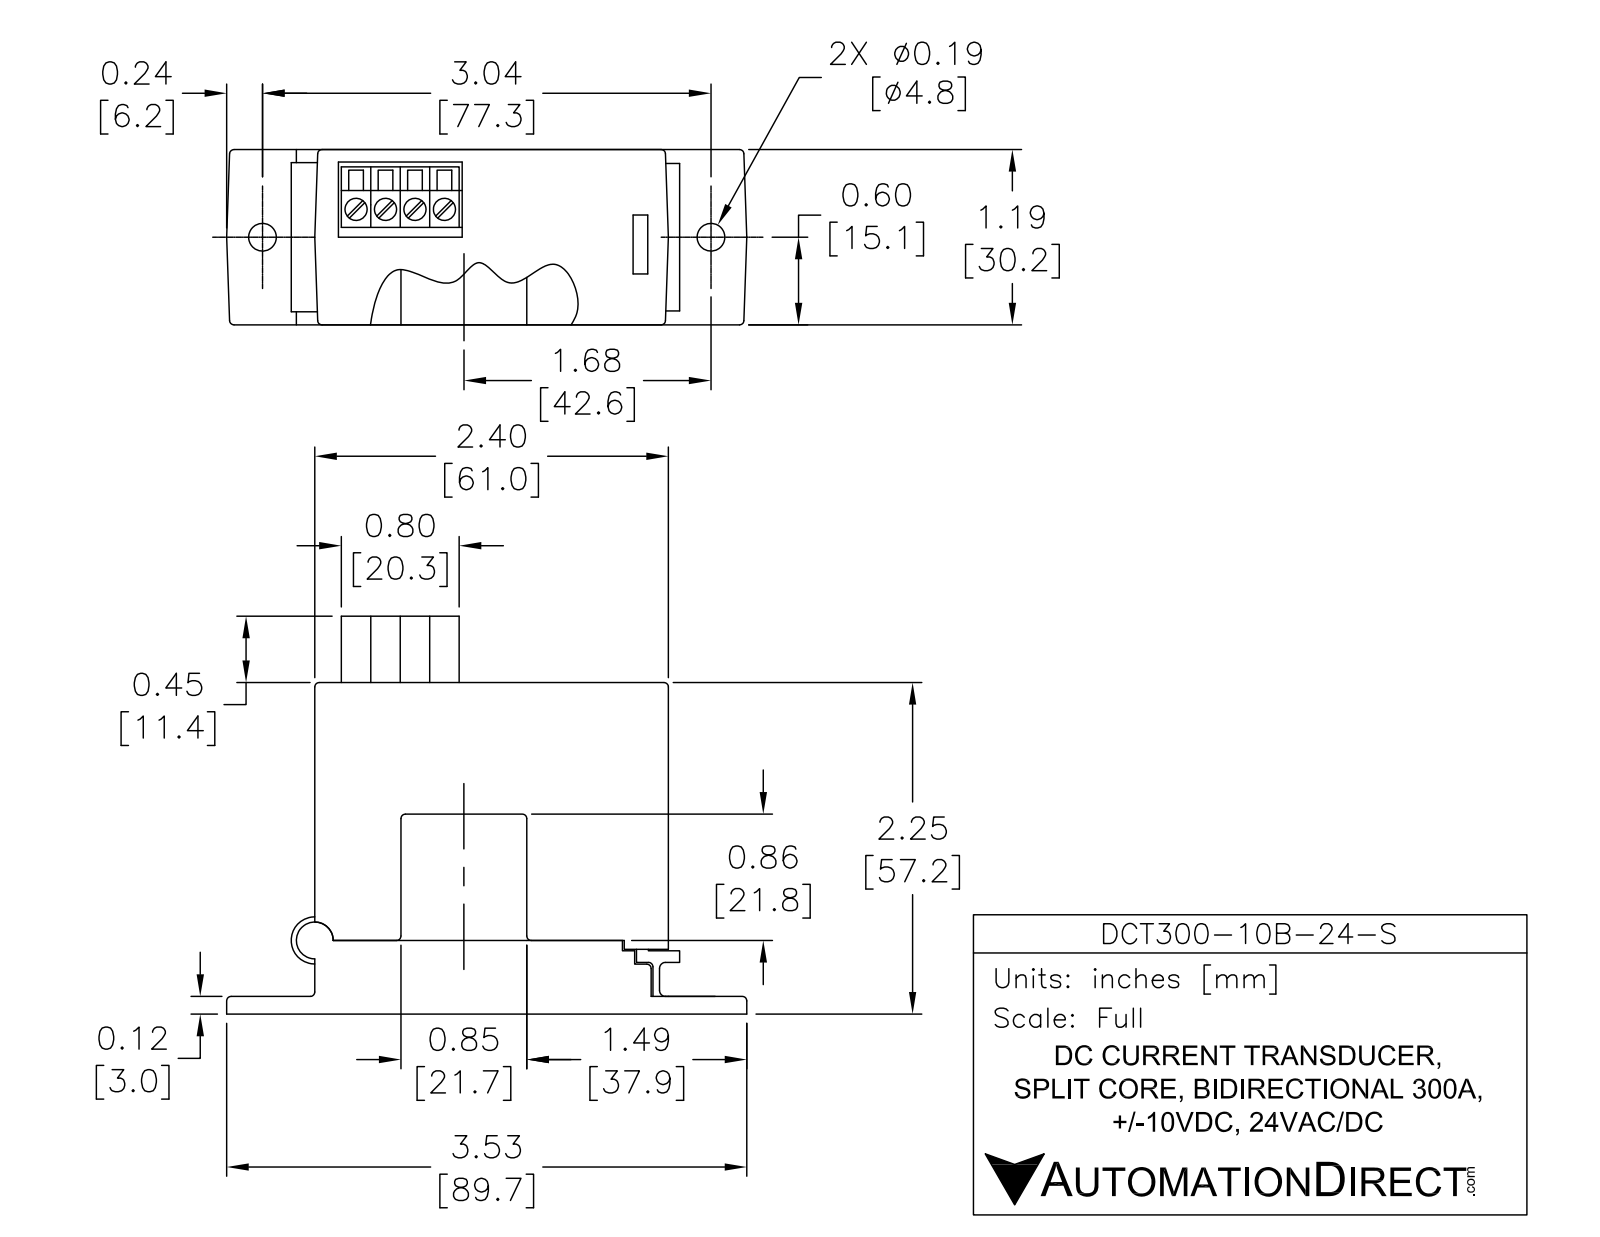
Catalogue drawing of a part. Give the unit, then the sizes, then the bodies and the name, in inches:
Units: inches
Overall size (bounding box): 3.531 × 2.7 × 1.189
Round holes (diameter × count): ⌀0.157 ×4, ⌀0.188 ×2, ⌀0.26 ×1
Round bosses / shafts (diameter × count): ⌀0.25 ×1
Partial cylindrical surfaces — rounded edges, fillets, slot ends (radius × count): R0.03 ×22, R0.16 ×1, R0.17 ×1
Main face-to-face distances: 1.189, 2.252, 0.5, 1.752, 2.399, 0.505, 1.747, 0.118, 0.382, 0.387
Hole centre spacings: 0.197, 0.398, 0.201, 0.596, 0.632, 0.822, 1.019, 1.213
Volume: 5.725 in³ · Surface area: 35.03 in²
Bodies: 4 solids, 158 faces (100 planar, 50 cylindrical, 8 other)
Part name (STEP PRODUCT): DCT300-10B-24-S
STEP written by: SolidWorks 2017 (AUTOMOTIVE_DESIGN)
